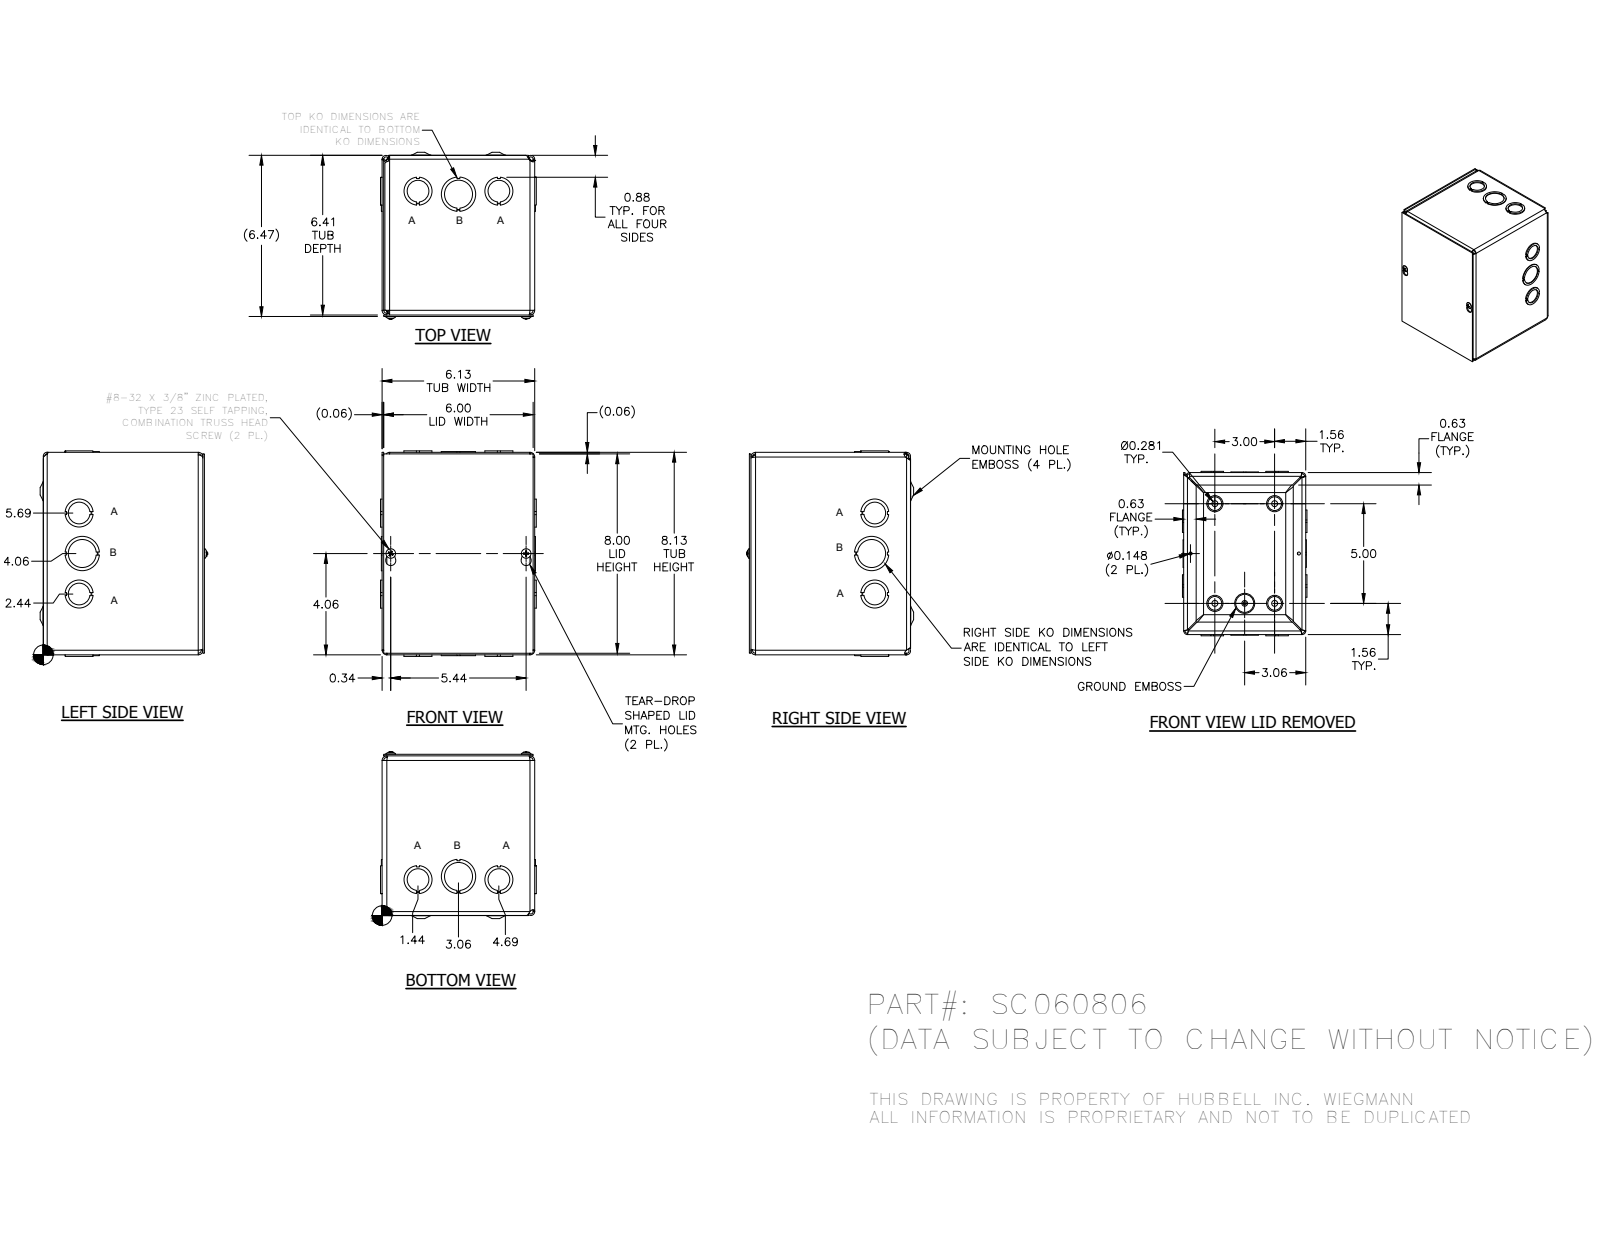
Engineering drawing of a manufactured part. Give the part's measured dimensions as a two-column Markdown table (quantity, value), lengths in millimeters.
| quantity | value |
| --- | --- |
| part name | SC0608BKP; SC060806WRA; SC0608LID; 34056 (+1 more) |
| STEP written by | Autodesk Inventor 2014 (AUTOMOTIVE_DESIGN) |
| units | millimeters |
| bodies | 20 solids, 630 faces (373 planar, 129 cylindrical, 128 other) |
| overall size | 209.53 × 170 × 158.72 |
| round holes (diameter × count) | 28.57 × 6, 7.62 × 4, 22.22 × 4, 3.76 × 2, 34.92 × 2, 4.19 × 1 |
| round bosses / shafts (diameter × count) | 9.75 × 2, 4.17 × 2, 5.8 × 1 |
| partial cylindrical surfaces (radius × count) | 3.17 × 10, 4.75 × 8, 1.4 × 4, 1.57 × 4, 2.38 × 4, 2.97 × 4, 3.15 × 4, 3.96 × 4 |
| main face-to-face distances | 1.57, 154, 161.12, 155.57, 162.69, 1.58, 152.43, 1.59, 162.71, 164.28 |
| hole center spacings | 38.1, 41.39, 41.4, 70.64, 70.65, 76.2, 82.55, 124.55 |
